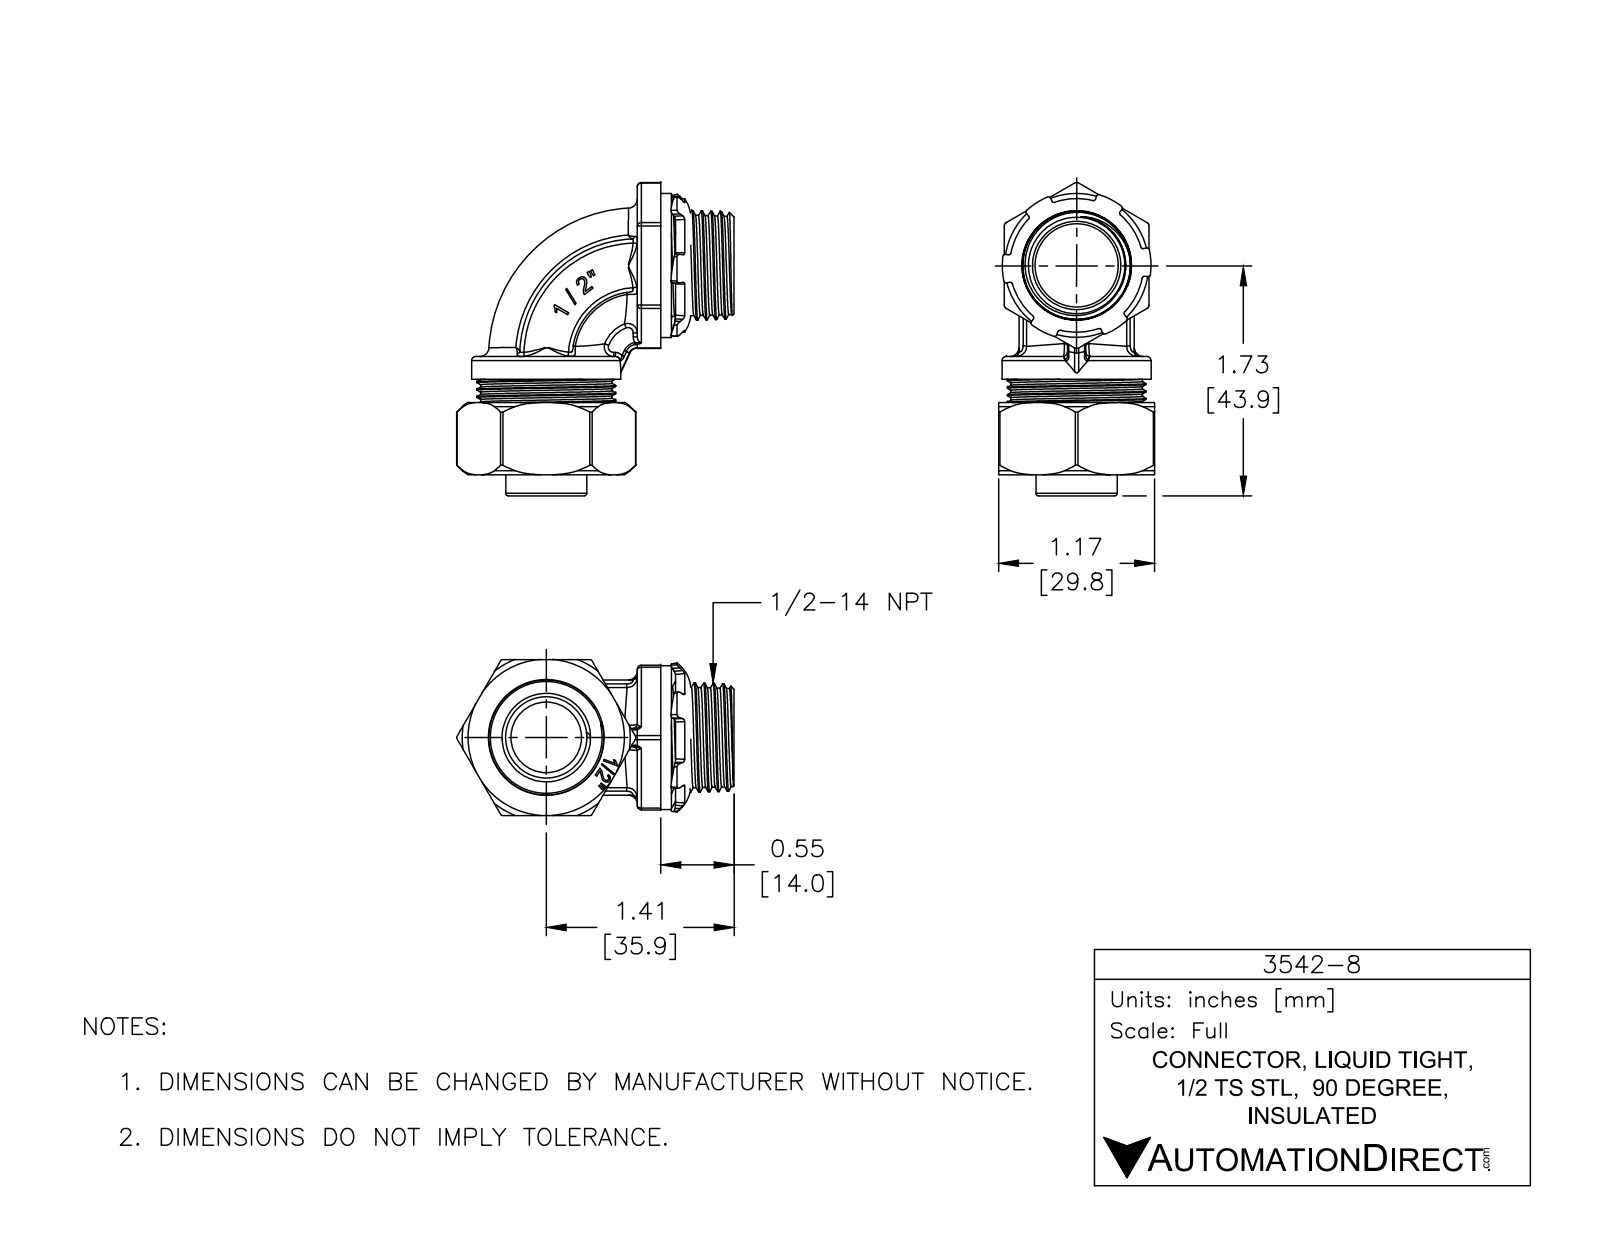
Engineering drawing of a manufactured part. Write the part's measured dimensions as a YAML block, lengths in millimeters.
part_name: "3402 GLAND RING_1-2; 3402 SEAL_1-2; 3512RAC INSULATION BUSHING_INSTALLED; 3422 90DEG BODY (+4 more)"
step_written_by: "SolidWorks 2014 (AUTOMOTIVE_DESIGN)"
units: millimeters
bodies: {solids: 7, faces: 629, planar: 236, cylindrical: 125, other: 268}
overall_size: [59.9, 54.5, 29.8]
volume: 17300
surface_area: 21260
round_holes:
  - {diameter: 17, count: 2}
  - {diameter: 2.7, count: 1}
  - {diameter: 13.4, count: 1}
  - {diameter: 14.5, count: 1}
  - {diameter: 15.8, count: 1}
  - {diameter: 21.5, count: 1}
  - {diameter: 21.8, count: 1}
  - {diameter: 22.1, count: 1}
  - {diameter: 22.9, count: 1}
  - {diameter: 25.8, count: 1}
round_bosses_or_shafts:
  - {diameter: 28.5, count: 1}
  - {diameter: 27.5, count: 1}
  - {diameter: 26.5, count: 1}
  - {diameter: 25.2, count: 1}
  - {diameter: 22.5, count: 1}
  - {diameter: 18, count: 1}
  - {diameter: 15.5, count: 1}
  - {diameter: 14.5, count: 1}
partial_cylinders:
  - {radius: 0.8, count: 17}
  - {radius: 0.2, count: 8}
  - {radius: 0.5, count: 6}
  - {radius: 0.5, count: 2}
  - {radius: 0.9, count: 2}
  - {radius: 0.2, count: 1}
  - {radius: 0.3, count: 1}
  - {radius: 0.6, count: 1}
face_to_face_distances: [29.8, 3.9, 25.9, 18.2, 2, 22, 13.8, 4.4, 1, 28.7]
hole_center_spacings: [12.7]
